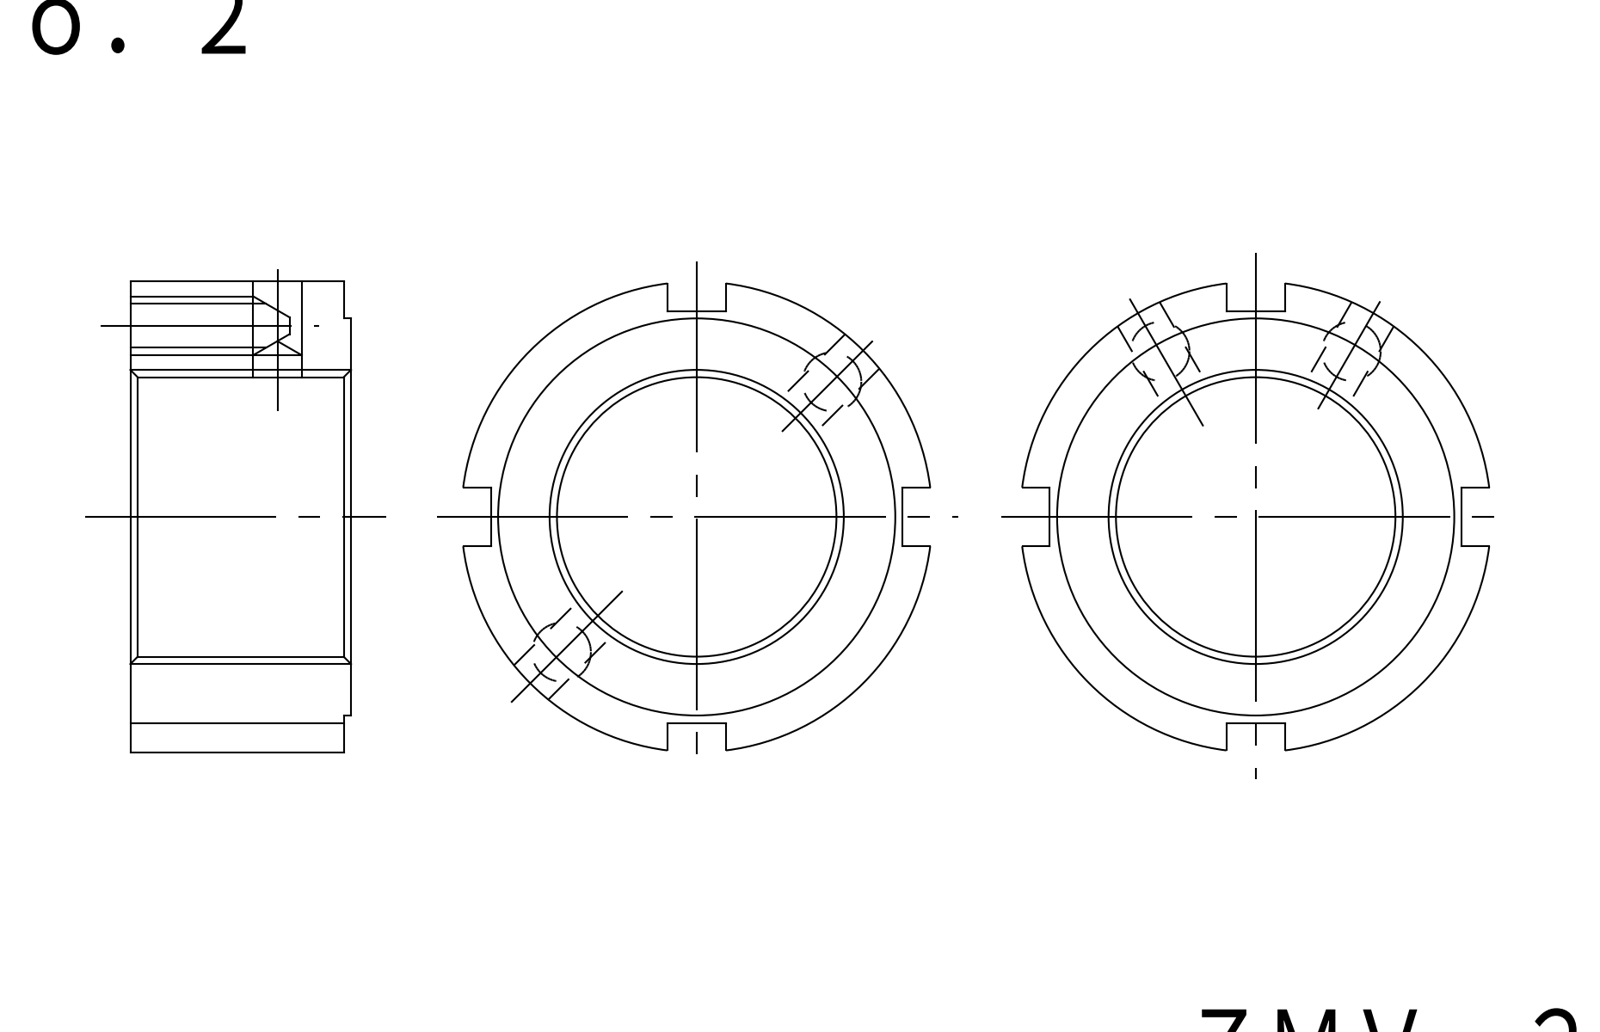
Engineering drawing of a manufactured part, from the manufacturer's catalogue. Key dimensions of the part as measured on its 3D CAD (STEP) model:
Part name (STEP PRODUCT): FKD ZMV20
STEP written by: Autodesk Inventor LT (CONFIG_CONTROL_DESIGN)
Units: millimetres
Bodies: 1 solid, 25 faces (15 planar, 10 cylindrical, 0 other)
Overall size (bounding box): 31.75 × 31.75 × 15
Volume: 6 537 mm³ · Surface area: 3 812 mm²
Round holes (diameter × count): ⌀3.24 ×2, ⌀3.3 ×2, ⌀20 ×1
Round bosses / shafts (diameter × count): ⌀32 ×1, ⌀27 ×1
Main face-to-face distances: 15, 12, 16, 0.5, 14.5, 28, 4
Hole centre spacings: 13, 25.99
